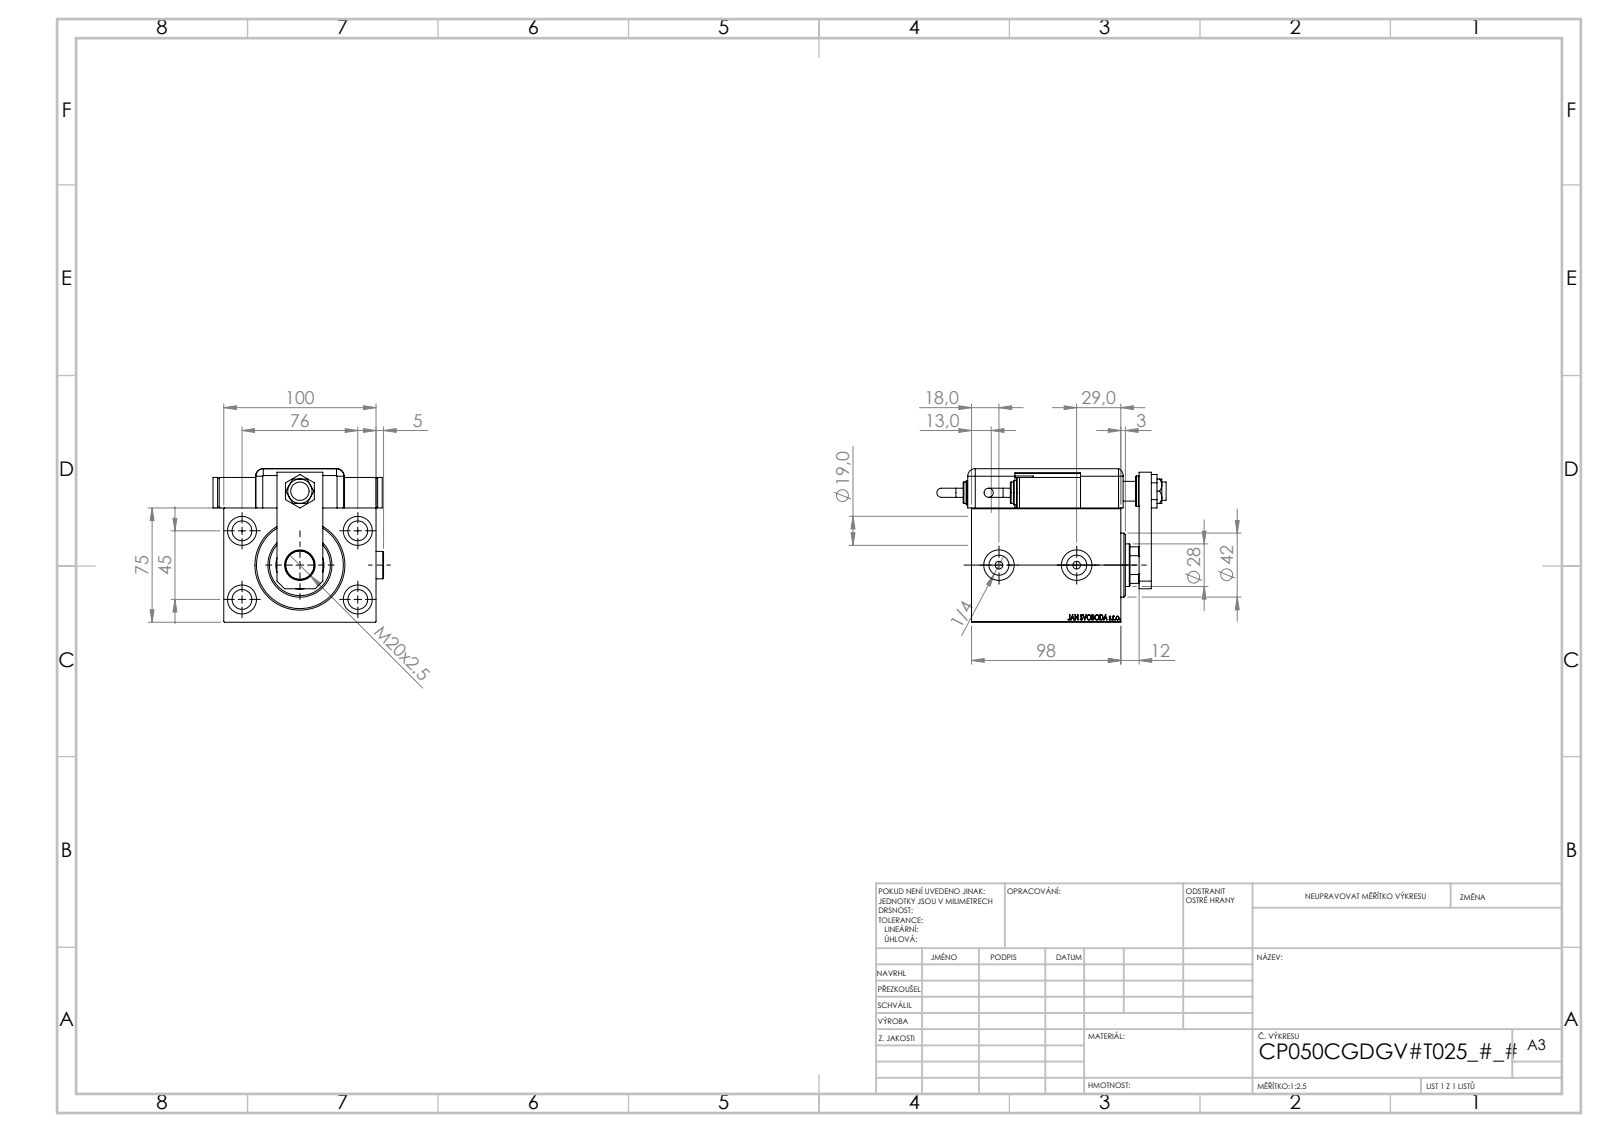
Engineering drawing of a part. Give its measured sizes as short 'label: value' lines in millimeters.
name: SWITCH Q; ZARAZKA_Q; Zatka_OIL_PORT; V450CM_C_Body (+7 more)
written by: SolidWorks 2019 (CONFIG_CONTROL_DESIGN)
unit: mm
bodies: 15 solids, 1303 faces (649 planar, 133 cylindrical, 521 other)
size: 150.46 × 111.9 × 100.8
volume: 770 831 mm³; area: 162 779 mm²
holes: 5× ⌀13, 4× ⌀19, 3× ⌀20, 2× ⌀4, 2× ⌀5, 2× ⌀8, 2× ⌀13.16, 1× ⌀12, 1× ⌀14, 1× ⌀18.5, 1× ⌀28, 1× ⌀31.5
bosses: 3× ⌀20, 2× ⌀18, 2× ⌀16, 2× ⌀14, 2× ⌀6, 1× ⌀42
rounds: 9× R5, 1× R10, 1× R13.5
face distances: 75, 3, 100, 98, 14, 20, 13.5, 84, 25.8, 100.8
hole spacings: 44.16, 45, 46.04, 76, 80.53, 88.32, 20, 48.5
